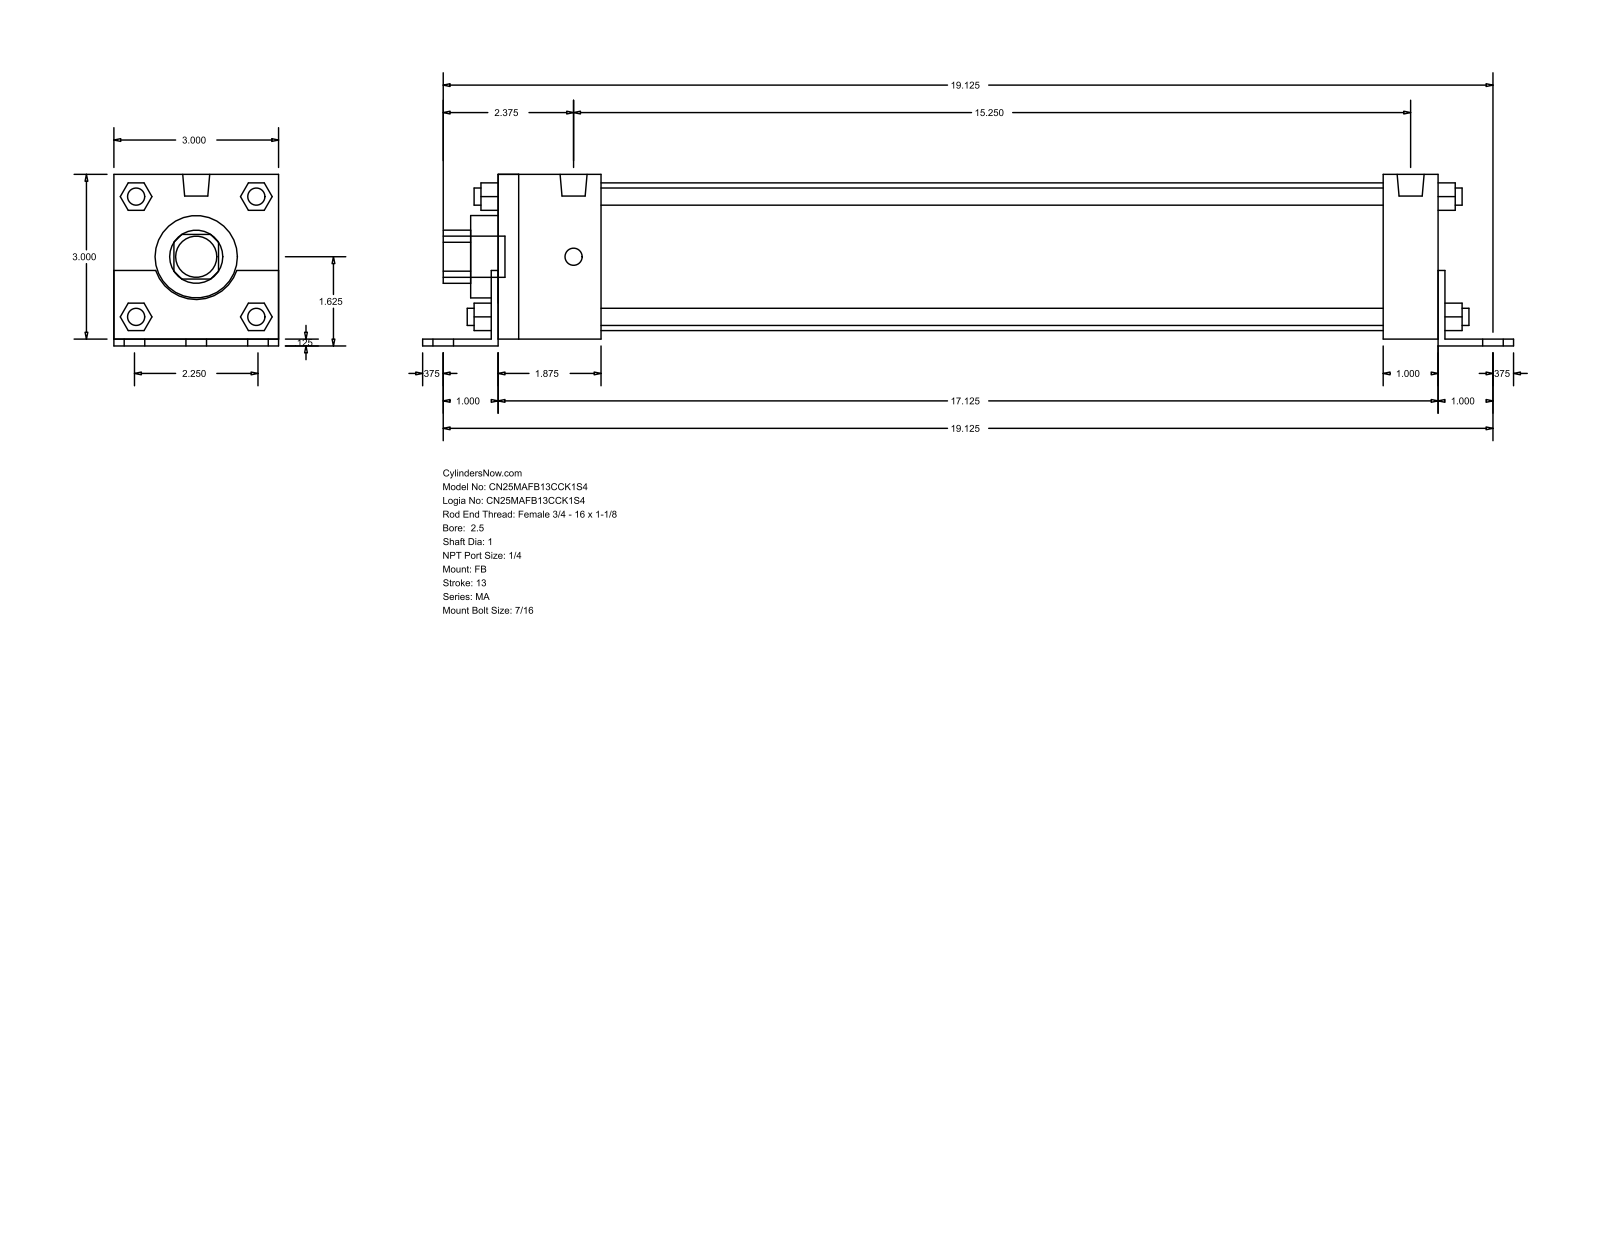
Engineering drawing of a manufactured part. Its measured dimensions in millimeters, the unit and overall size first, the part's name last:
Units: millimetres
Overall size (bounding box): 504.82 × 79.38 × 76.2
Round holes (diameter × count): ⌀25.4 ×1, ⌀38.1 ×1, ⌀68.33 ×1
Round bosses / shafts (diameter × count): ⌀7.94 ×8, ⌀11.11 ×6, ⌀12.49 ×2, ⌀19.05 ×1
Partial cylindrical surfaces — rounded edges, fillets, slot ends (radius × count): R12.29 ×1, R19.81 ×1
Main face-to-face distances: 76.2, 3.17, 79.37, 438.15, 434.98, 12.7, 25.4, 28.57, 47.63, 387.35
Bodies: 0 solids, 140 faces (105 planar, 35 cylindrical, 0 other)
Part name (STEP PRODUCT): MA_FB__0250_1
STEP written by: GSSL Pune (CONFIG_CONTROL_DESIGN)
